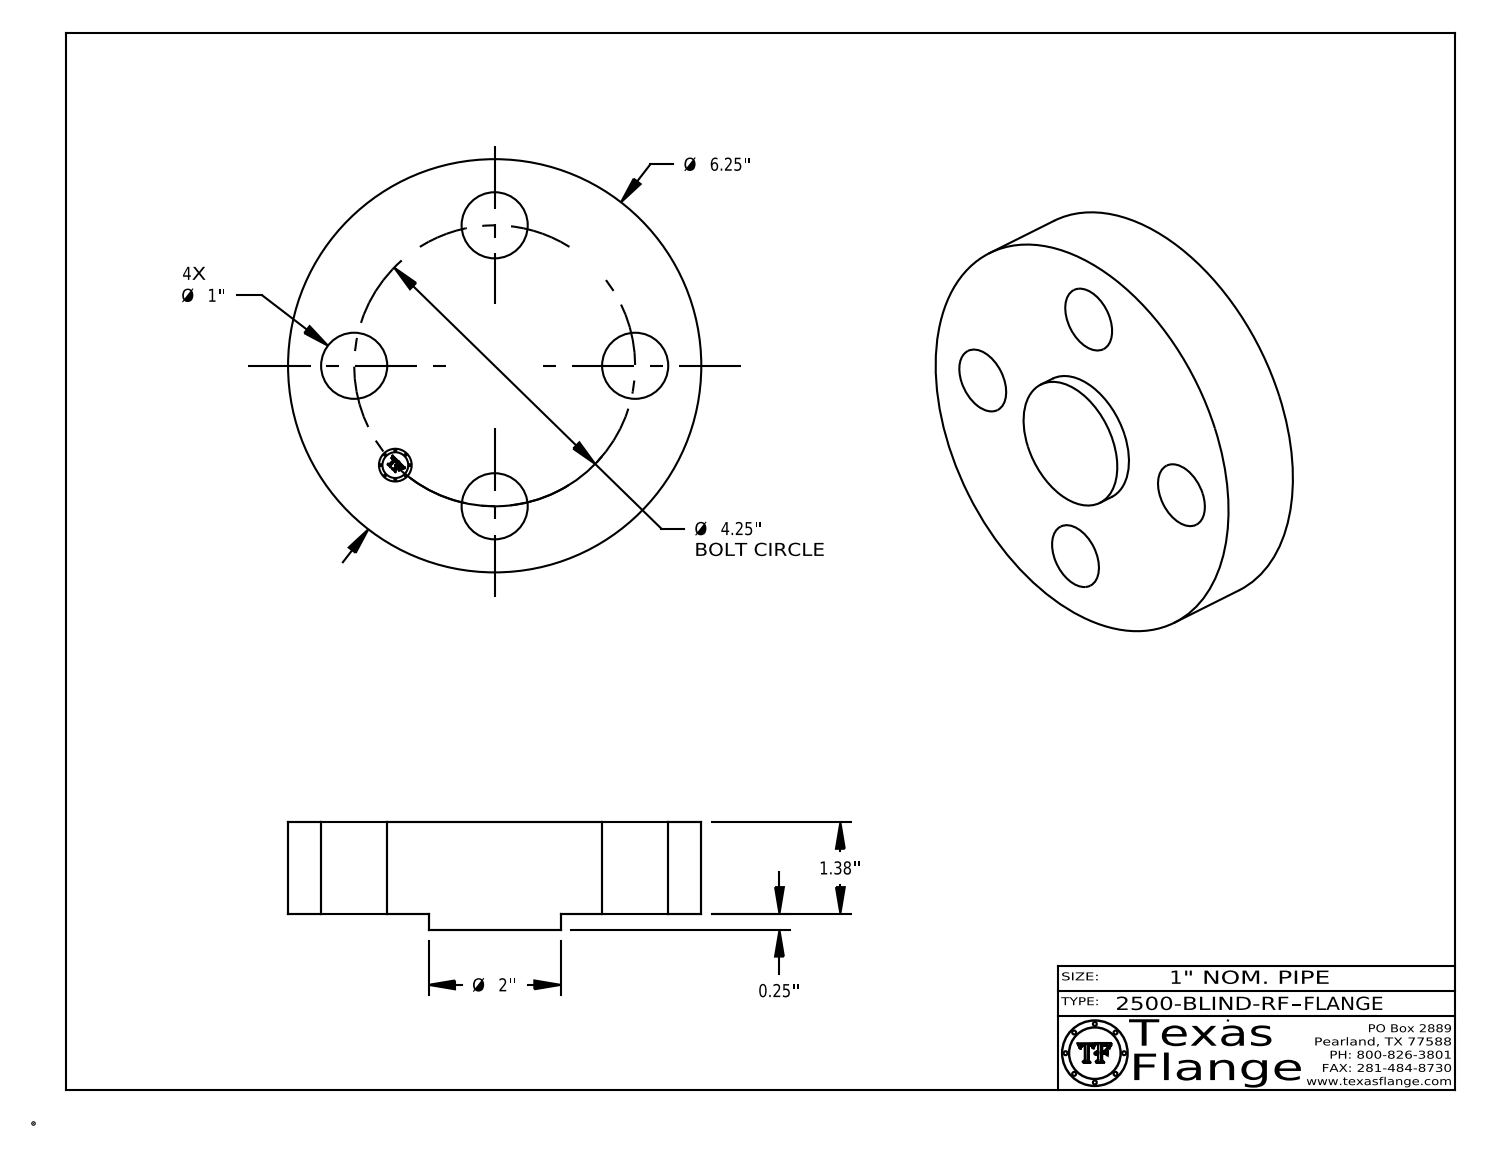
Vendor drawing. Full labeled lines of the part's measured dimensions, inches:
Part name (STEP PRODUCT): 2500-BLIND-RF
STEP written by: CATIA V5 STEP AP214 (AUTOMOTIVE_DESIGN)
Units: inches
Bodies: 1 solid, 400 faces (368 planar, 32 cylindrical, 0 other)
Overall size (bounding box): 6.25 × 6.25 × 1.63
Volume: 38.79 in³ · Surface area: 101.2 in²
Round holes (diameter × count): ⌀1 ×4, ⌀0.495 ×1
Round bosses / shafts (diameter × count): ⌀0.03 ×8, ⌀6.25 ×1, ⌀2 ×1, ⌀0.39 ×1
Main face-to-face distances: 1.38, 0.25, 1.63, 1.615, 1.365, 0.015, 0.148, 0.144, 0.027, 0.096
Hole centre spacings: 3.006, 1.626, 3.927, 4.25
